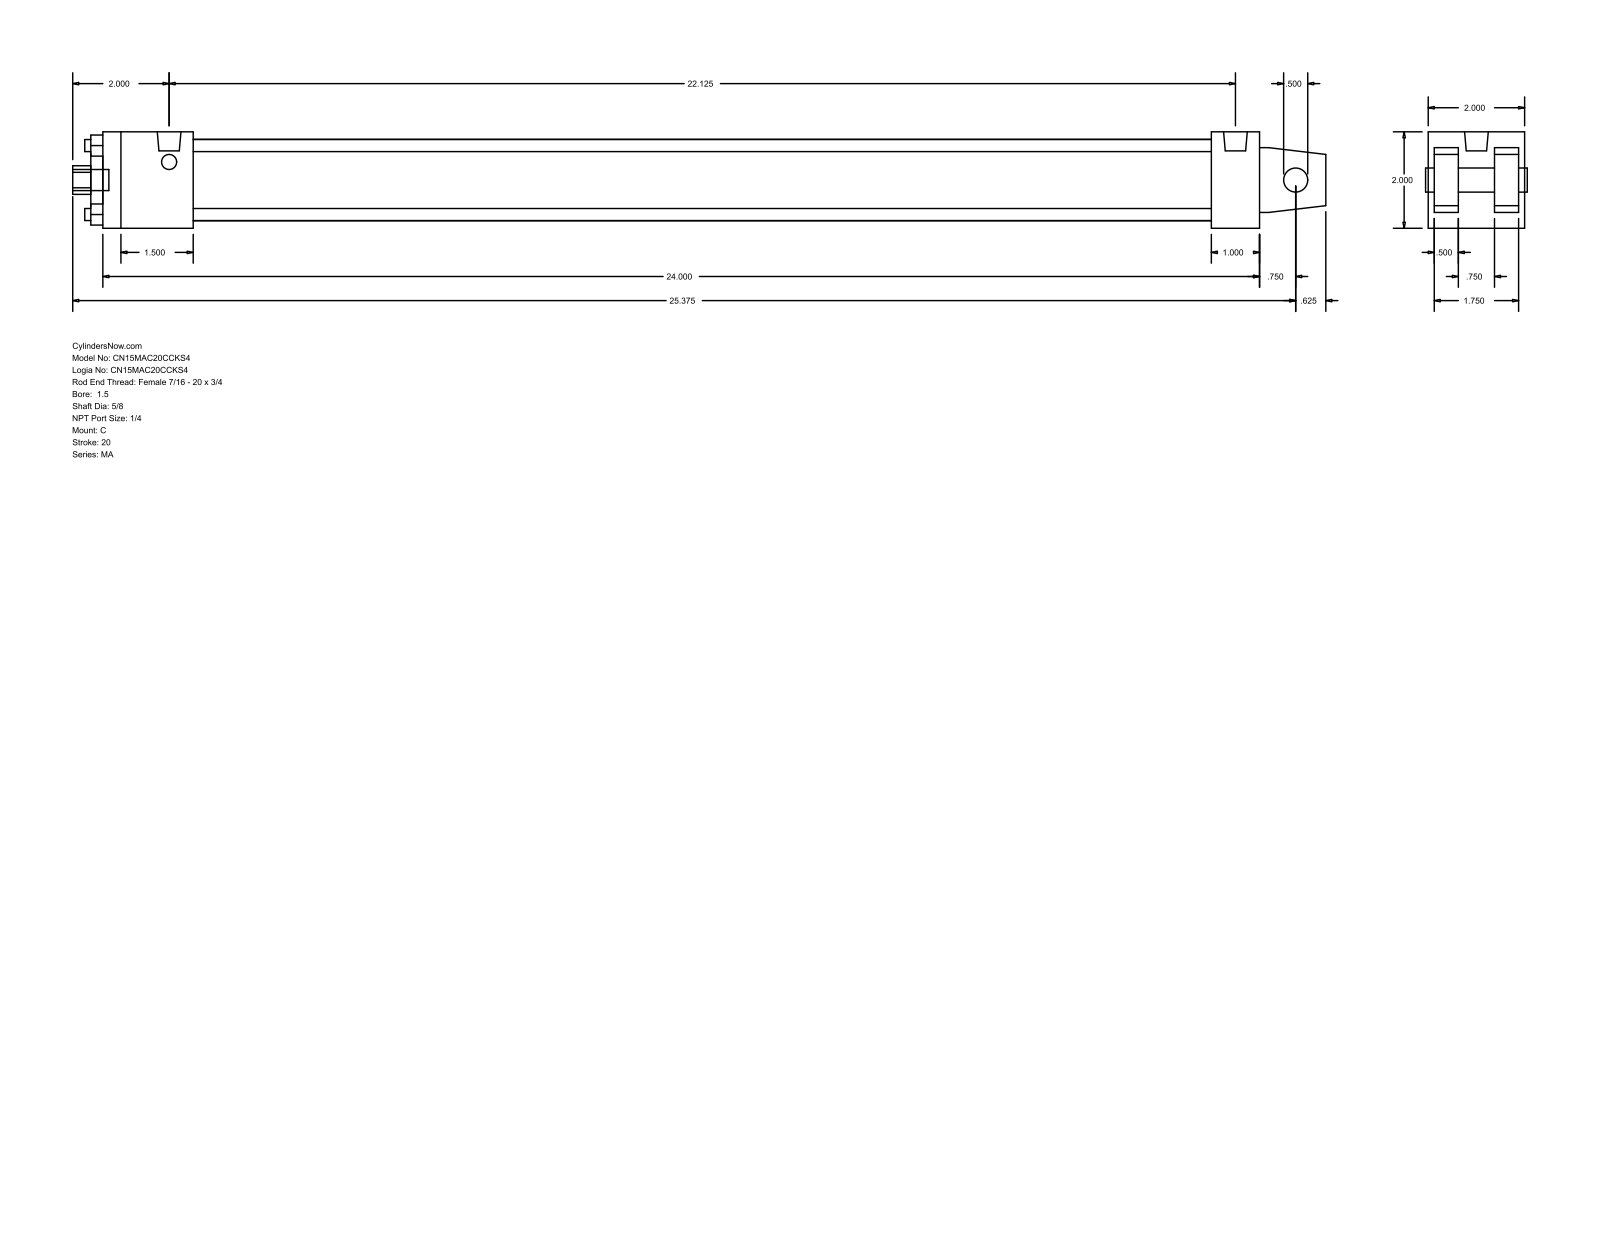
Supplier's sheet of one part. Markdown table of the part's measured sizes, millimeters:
| quantity | value |
| --- | --- |
| part name | MA_C__0150_0.625 |
| STEP written by | GSSL Pune (CONFIG_CONTROL_DESIGN) |
| units | millimeters |
| bodies | 0 solids, 103 faces (76 planar, 27 cylindrical, 0 other) |
| overall size | 660.4 × 50.8 × 50.8 |
| round holes (diameter × count) | 6.35 × 4, 12.7 × 1, 15.88 × 1, 28.57 × 1, 42.93 × 1 |
| round bosses / shafts (diameter × count) | 7.94 × 4, 12.49 × 2, 11.11 × 1 |
| partial cylindrical surfaces (radius × count) | 7.54 × 1 |
| main face-to-face distances | 50.8, 12.7, 3.17, 15.87, 34.93, 47.63, 31.76, 609.6, 584.2, 25.4 |
| hole center spacings | 25.68, 36.32, 51.36 |
